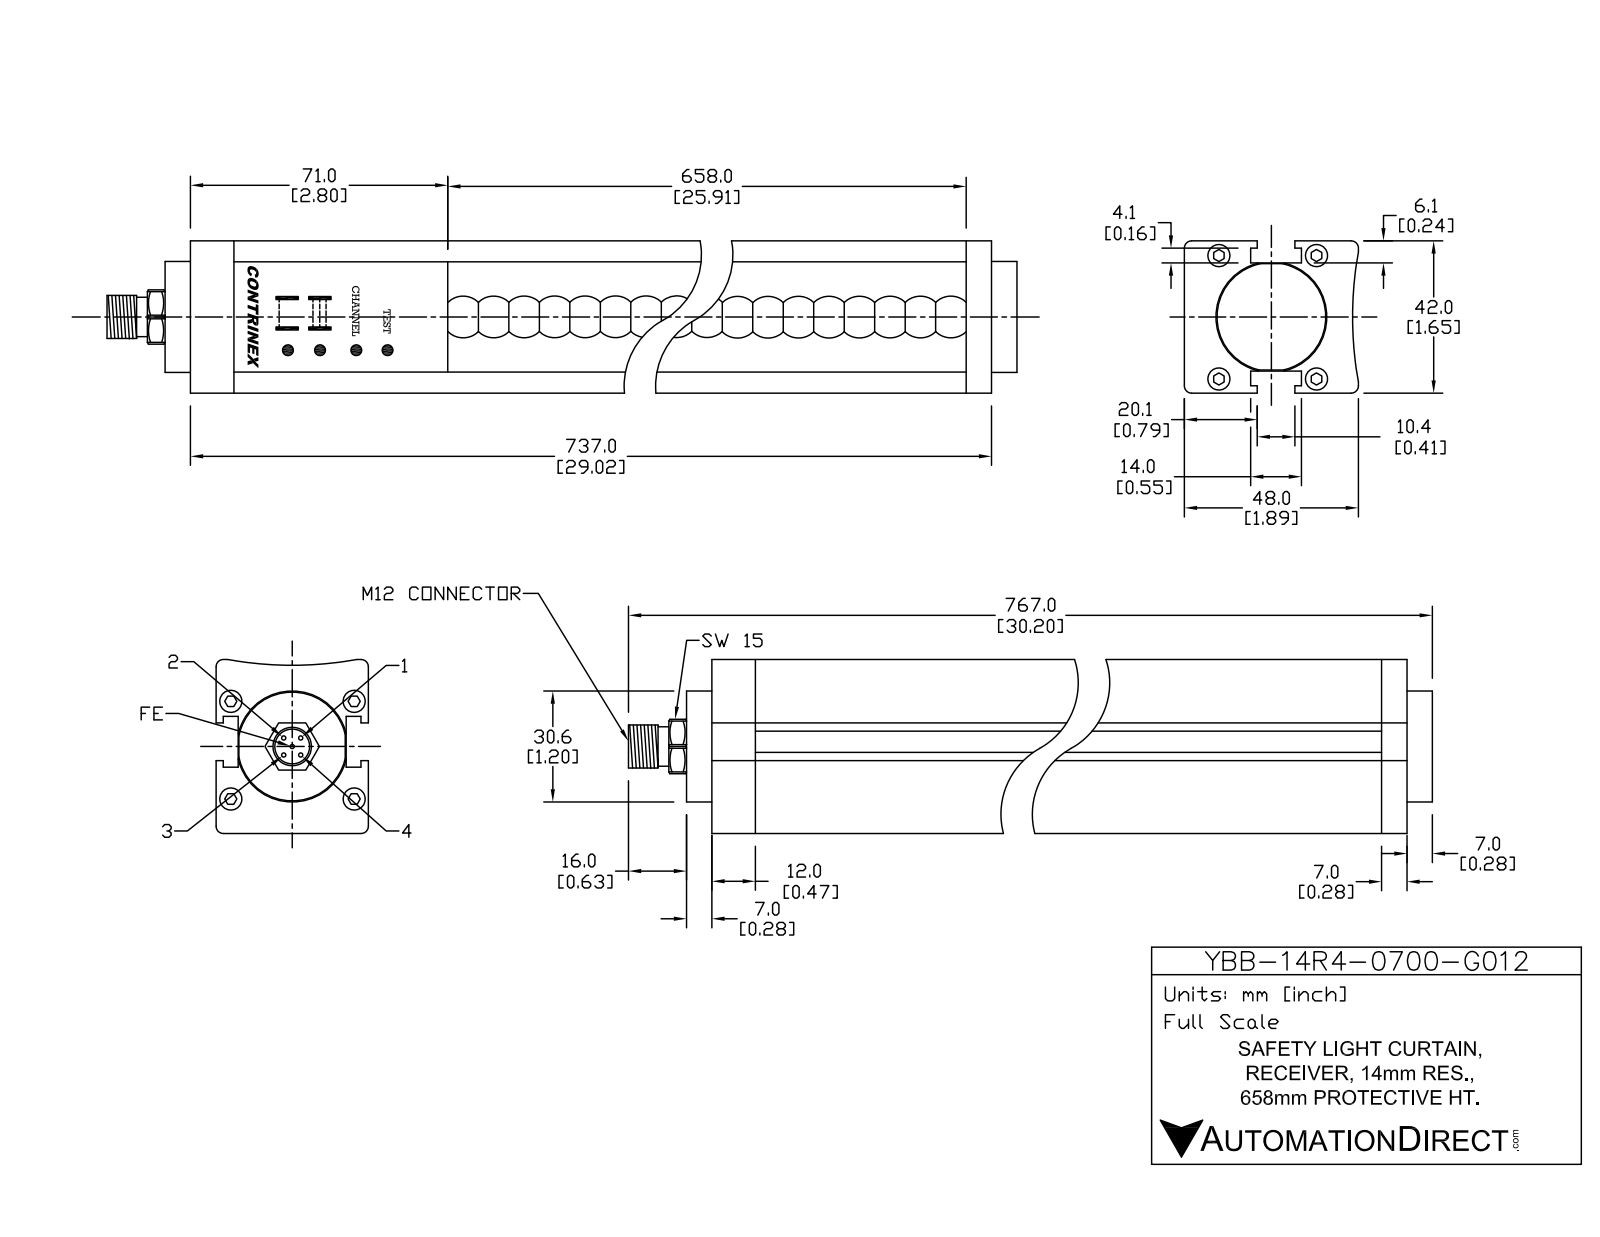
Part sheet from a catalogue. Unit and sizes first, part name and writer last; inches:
Units: inches
Overall size (bounding box): 30.197 × 1.89 × 1.654
Round holes (diameter × count): ⌀0.236 ×4, ⌀0.335 ×1, ⌀1.26 ×1
Round bosses / shafts (diameter × count): ⌀0.039 ×5, ⌀0.217 ×4, ⌀1.205 ×1, ⌀0.472 ×1, ⌀0.413 ×1
Partial cylindrical surfaces — rounded edges, fillets, slot ends (radius × count): R0.039 ×48, R0.02 ×4, R0.022 ×2, R0.323 ×1, R3.937 ×1
Main face-to-face distances: 0.248, 1.406, 1.654, 1.157, 0.551, 0.677, 1.228, 0.618, 1.169, 1.846
Hole centre spacings: 0.828, 0.88, 1.059, 1.339, 1.707
Volume: 81.16 in³ · Surface area: 271.1 in²
Bodies: 19 solids, 440 faces (208 planar, 168 cylindrical, 64 other)
Part name (STEP PRODUCT): YBB-14R4-0700-G012
STEP written by: SolidWorks 2016 (AUTOMOTIVE_DESIGN)
